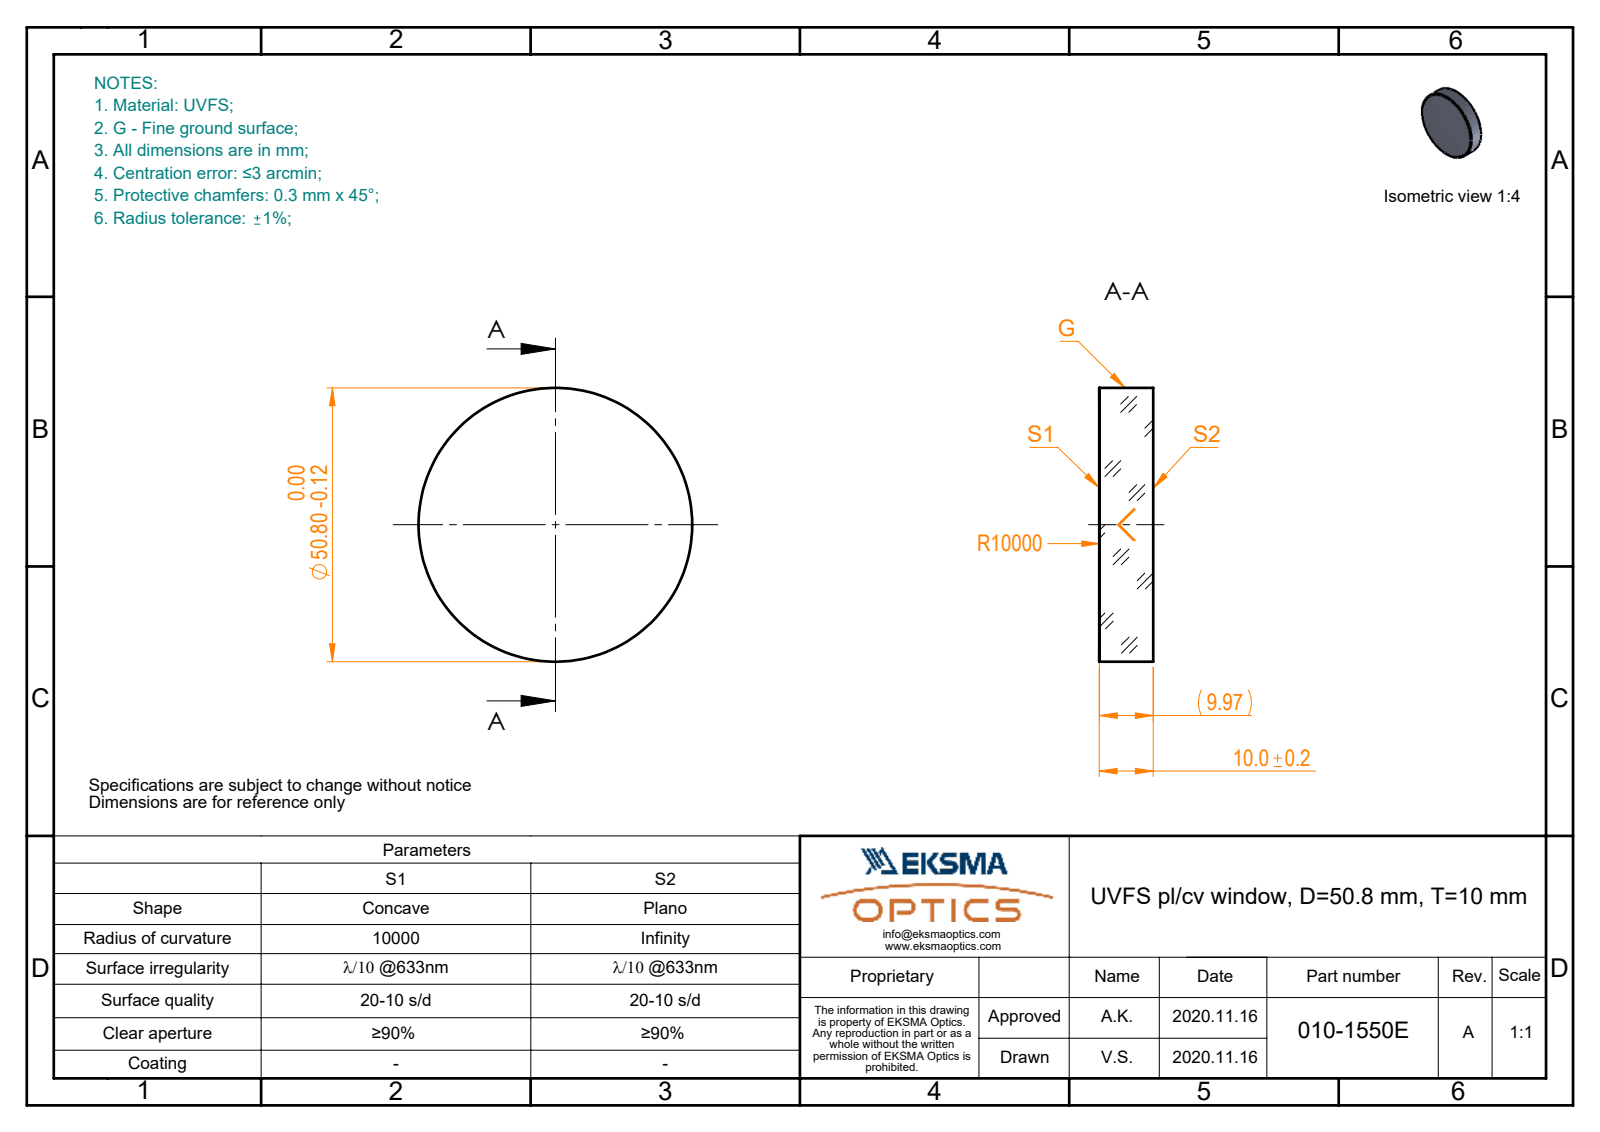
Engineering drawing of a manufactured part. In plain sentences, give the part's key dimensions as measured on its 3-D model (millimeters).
The part is named "010-1550E_UVFS_PCV_window". Its 3-D file was written by "SolidWorks 2019 (CONFIG_CONTROL_DESIGN)". It is 1 solid with 5 faces: 1 planar, 2 cylindrical and 2 other. Overall it measures 50.8 by 50.8 by 10 millimeters. Its volume is 20 236 cubic millimeters and its surface area 5 650 square millimeters. Round bosses or shafts: 1 of diameter 50.8.
